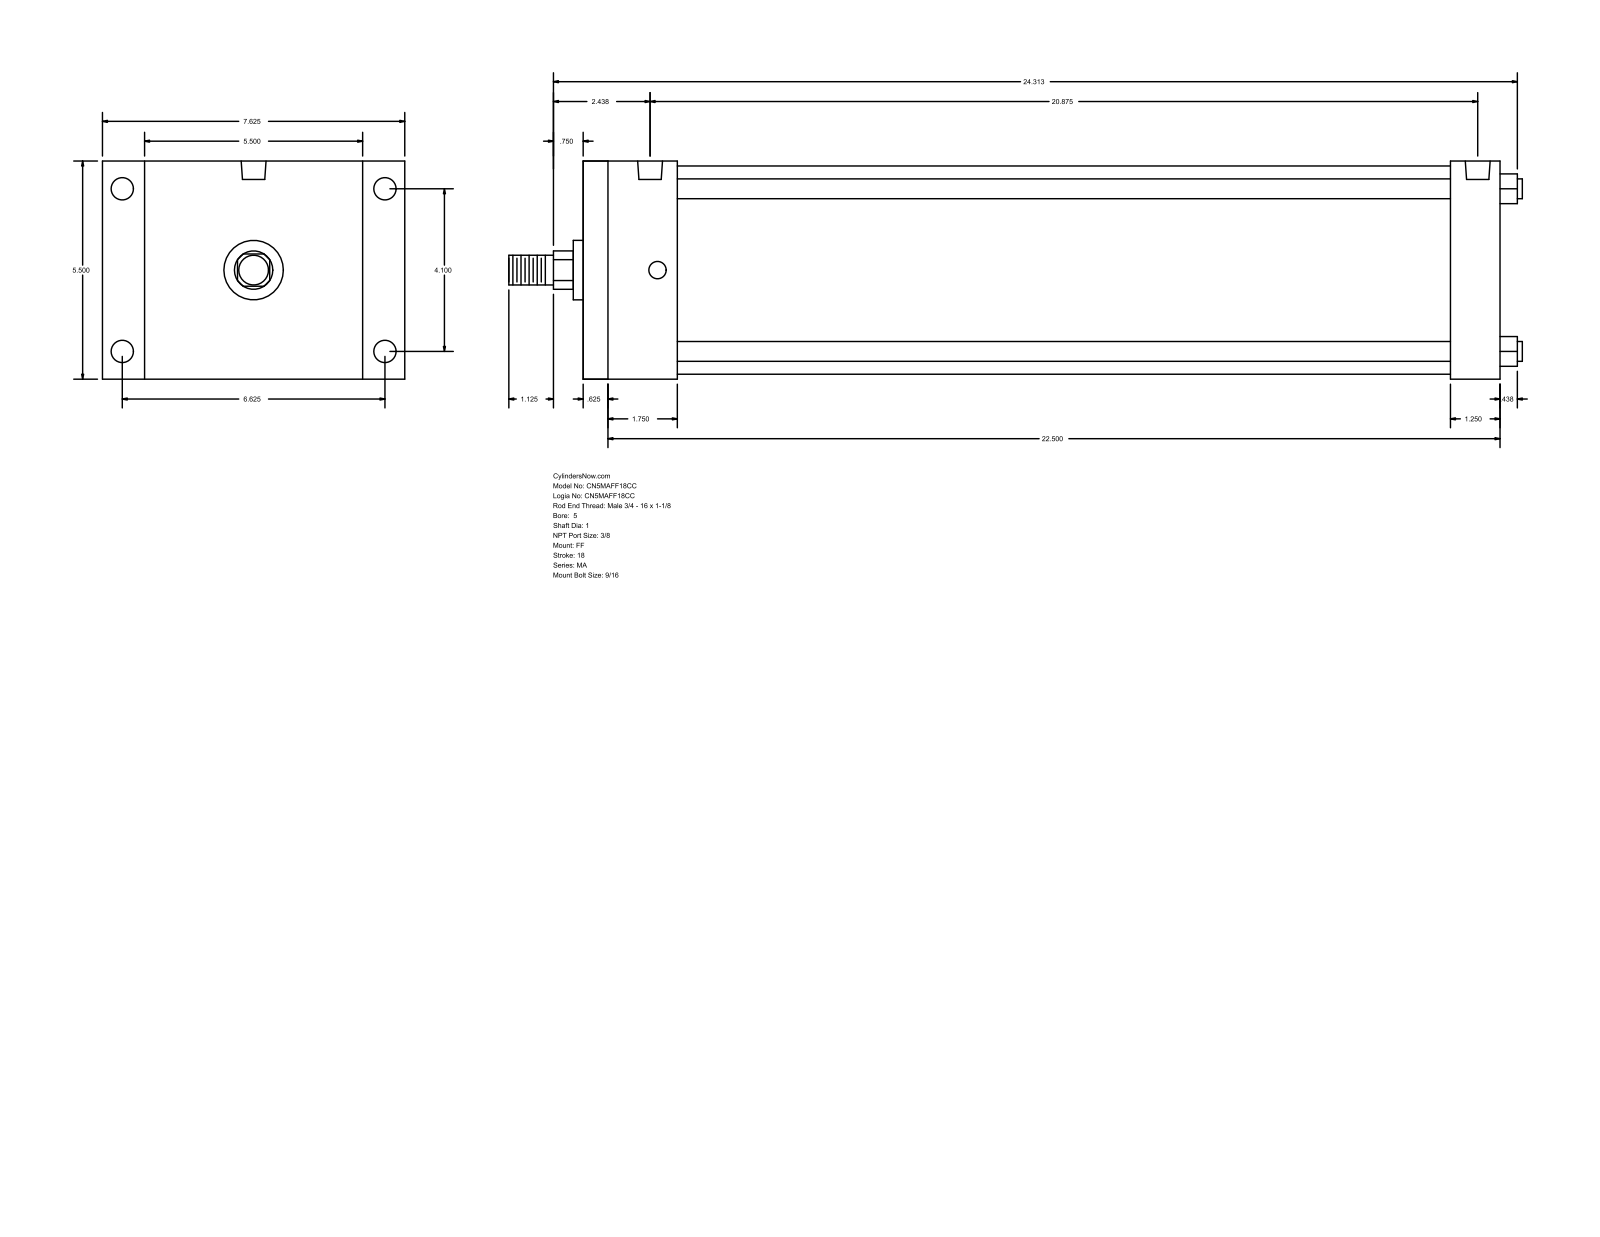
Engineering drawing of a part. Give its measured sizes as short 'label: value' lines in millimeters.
name: MA_FF__0500_1
written by: GSSL Pune (CONFIG_CONTROL_DESIGN)
unit: mm
bodies: 0 solids, 92 faces (64 planar, 28 cylindrical, 0 other)
size: 649.29 × 193.68 × 139.7
holes: 4× ⌀11.11, 4× ⌀14.29, 2× ⌀15.93
bosses: 4× ⌀12.7, 1× ⌀133.35, 1× ⌀38.1, 1× ⌀25.4, 1× ⌀19.05
rounds: 1× R12.29
face distances: 139.7, 587.37, 15.87, 571.5, 555.62, 539.75, 31.75, 60.33, 44.46, 495.29
hole spacings: 4.76, 104.14, 168.28, 197.9, 520.71, 525.47, 530.23
